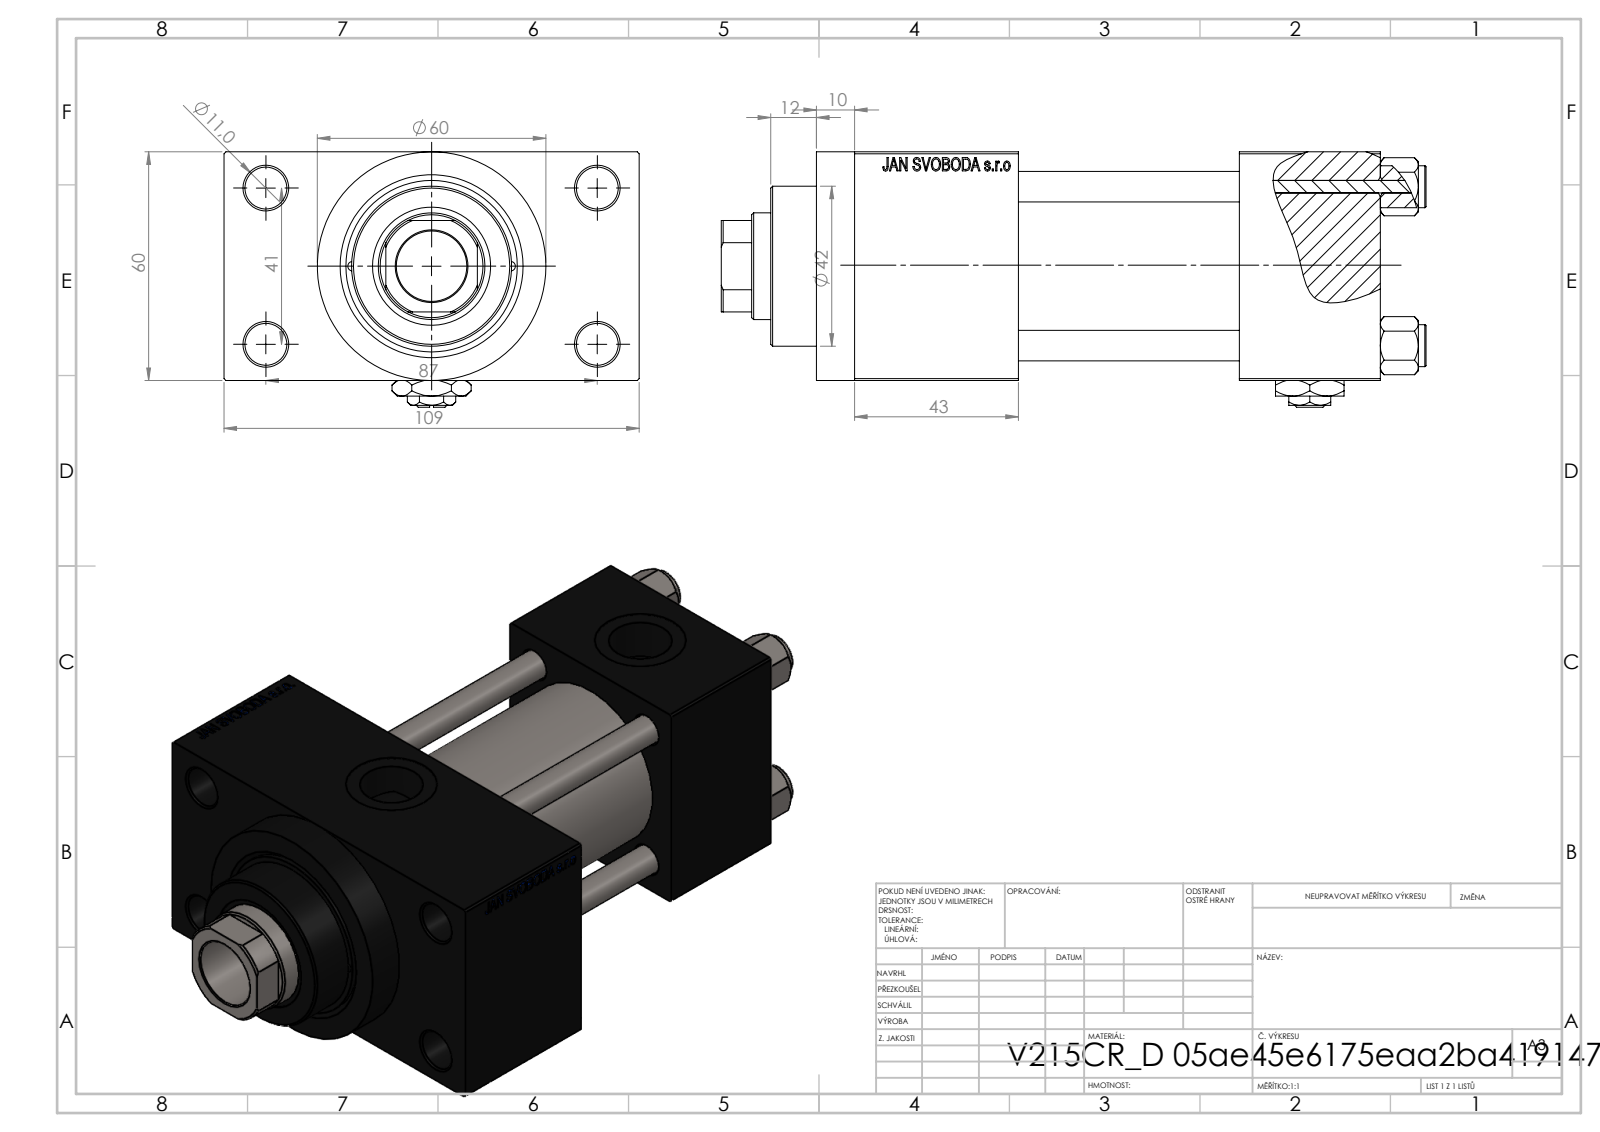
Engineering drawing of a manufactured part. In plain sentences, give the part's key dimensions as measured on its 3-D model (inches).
The part is named "V215_VC_A; V215CR_D_Body; NUT_M5_D; V215CR_D_TYCINKA (+2 more)". Its 3-D file was written by "SolidWorks 2019 (CONFIG_CONTROL_DESIGN)". It is 12 solids with 1168 faces: 526 planar, 100 cylindrical and 542 other. Overall it measures 7.283 by 4.291 by 2.638 inches. Its volume is 32.47 cubic inches and its surface area 200.8 square inches. Round holes: 4 of diameter 0.315, 4 of diameter 0.433, 2 of diameter 0.098, 2 of diameter 0.276, 2 of diameter 0.656, 2 of diameter 0.945, 1 of diameter 0.728, 1 of diameter 1.102, 1 of diameter 1.22, 1 of diameter 1.575, 1 of diameter 1.772. Round bosses or shafts: 4 of diameter 0.433, 1 of diameter 2.362, 1 of diameter 1.811, 1 of diameter 1.654. Partial cylindrical surfaces (rounded edges, fillets, slot ends): 1 of radius 0.531. The main face-to-face distances are 2.362, 3.327, 0.965, 2.283, 1.457, 3.74, 5.433, 3.976, 1.693, 4.291. The hole center spacings are 0.821, 0.892, 1.161, 1.206, 1.642, 1.832, 1.856, 1.893.
